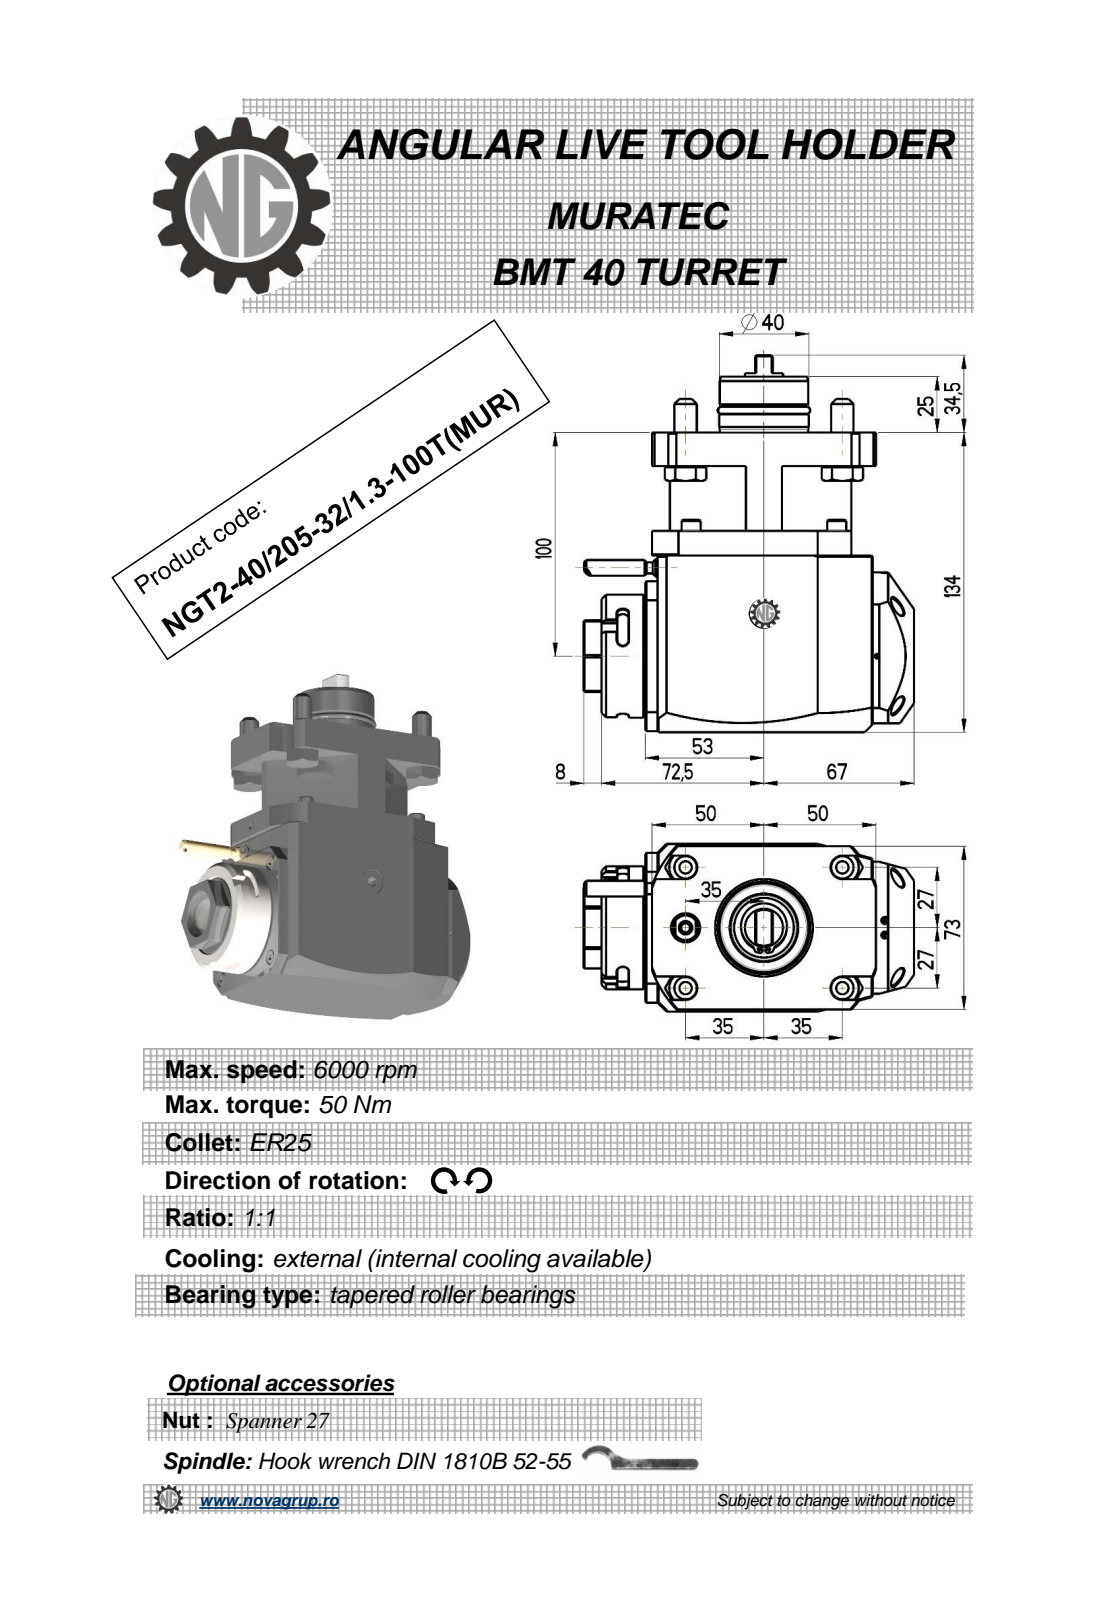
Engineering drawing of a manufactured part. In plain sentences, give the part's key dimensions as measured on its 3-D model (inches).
The part is named "NGT2_40_201_32_1_3_100T_MUR". Its 3-D file was written by "PRO/ENGINEER BY PARAMETRIC TECHNOLOGY CORPORATION, 2010280 (CONFIG_CONTROL_DESIGN)". It is 2 solids with 365 faces: 189 planar, 74 cylindrical and 102 other. Overall it measures 6.634 by 5.807 by 2.953 inches. Its volume is 61.08 cubic inches and its surface area 128.8 square inches. Round holes: 1 of diameter 0.098, 1 of diameter 0.118, 1 of diameter 0.165, 1 of diameter 0.354, 1 of diameter 0.906. Round bosses or shafts: 4 of diameter 0.575, 4 of diameter 0.394, 1 of diameter 2.165, 1 of diameter 1.85, 1 of diameter 1.575, 1 of diameter 1.555, 1 of diameter 1.551, 1 of diameter 1.394. Partial cylindrical surfaces (rounded edges, fillets, slot ends): 6 of radius 0.098, 4 of radius 0.207, 2 of radius 7.087, 1 of radius 0.236, 1 of radius 0.965, 1 of radius 1.476, 1 of radius 2.106. The main face-to-face distances are 2.953, 5.276, 0.039, 2.913, 2.48, 3.543, 1.732, 0.591, 1.142, 4.685. The hole center spacings are 1.701.
